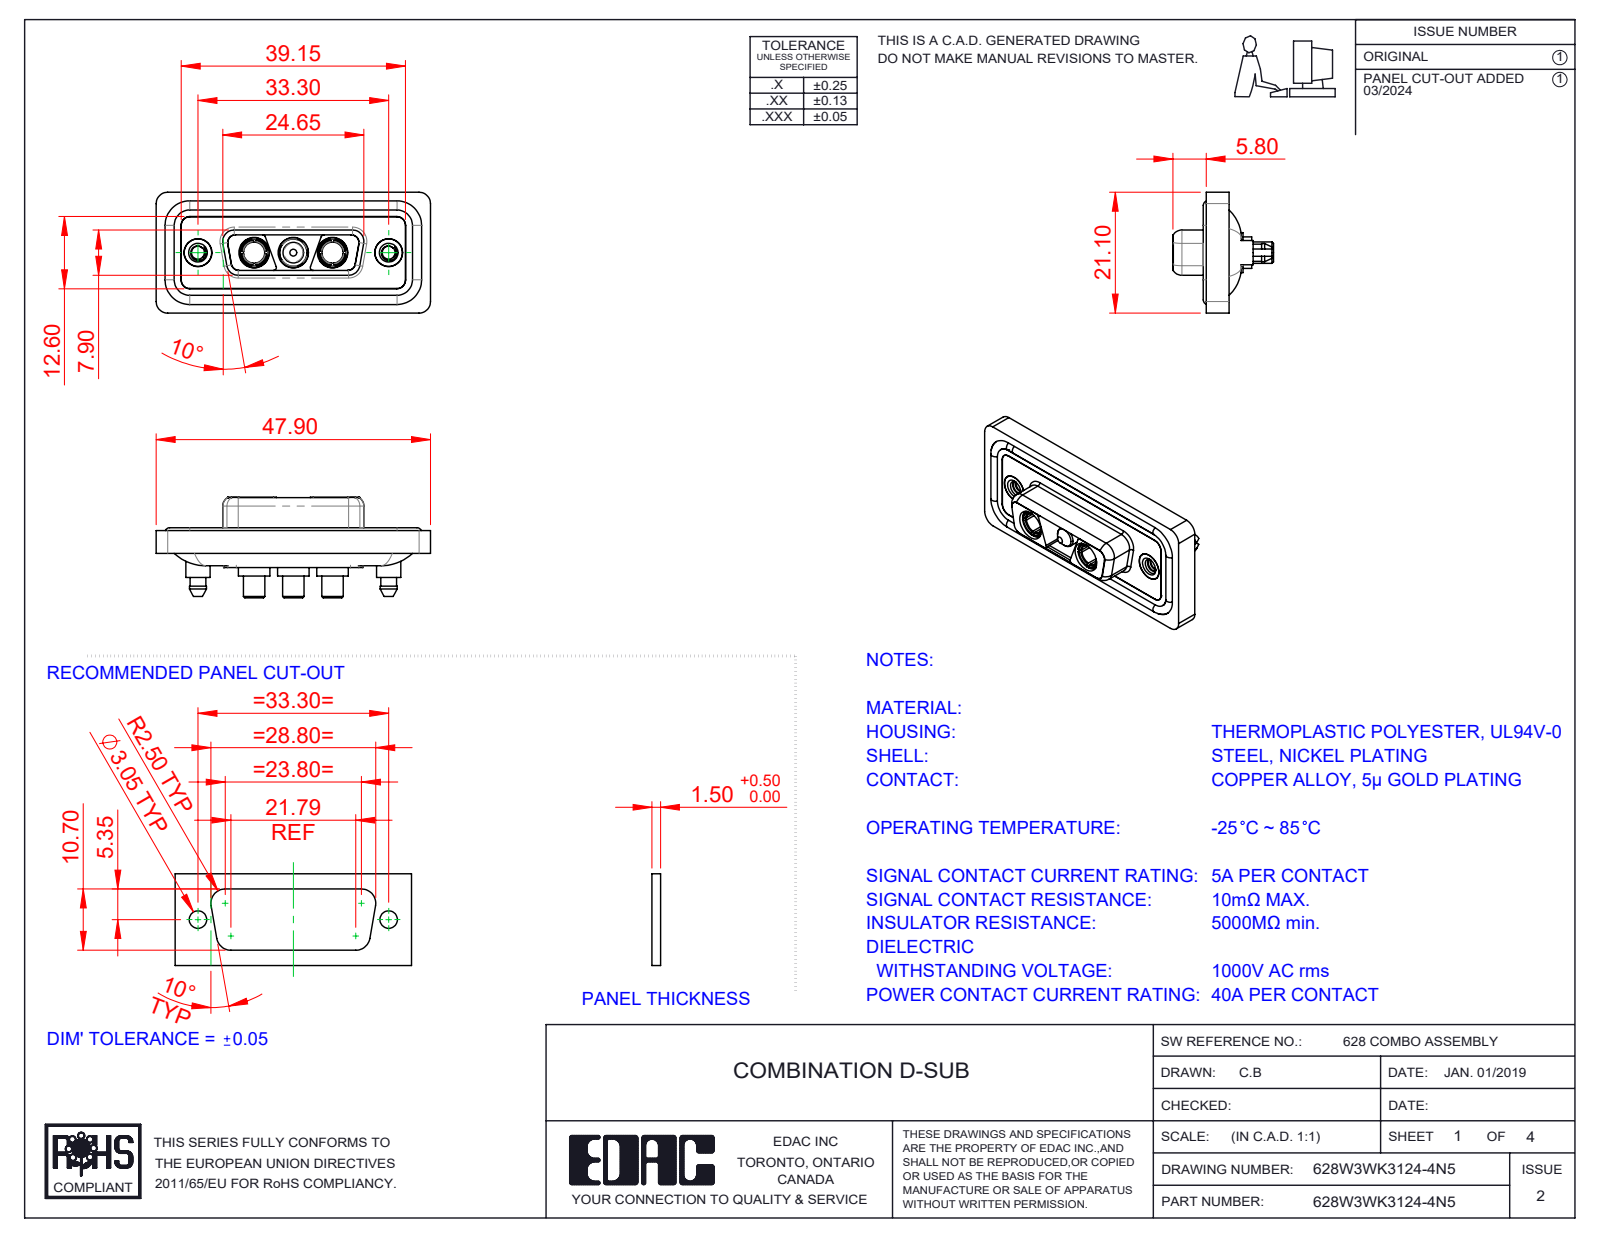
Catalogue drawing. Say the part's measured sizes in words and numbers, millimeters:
The part is named "Power Pin_40A S; 628Combo Housing_3WK3; 628Combo Shell Rear_15 Contacts; Power Socket_40A S (+4 more)". Its 3-D file was written by "SolidWorks 2023 (CONFIG_CONTROL_DESIGN)". It is 13 solids with 633 faces: 194 planar, 290 cylindrical and 149 other. Overall it measures 47.9 by 21.1 by 17.55 millimeters. Its volume is 6 067 cubic millimeters and its surface area 9 870 square millimeters. Round holes: 5 of diameter 4.85, 3 of diameter 5.3, 2 of diameter 2.26, 2 of diameter 3.7, 2 of diameter 4, 2 of diameter 4.05, 2 of diameter 5. Round bosses or shafts: 4 of diameter 1.6, 3 of diameter 5.5, 3 of diameter 5.2, 3 of diameter 4.75, 3 of diameter 3.75, 2 of diameter 5.4, 2 of diameter 4.96, 2 of diameter 4.95. Partial cylindrical surfaces (rounded edges, fillets, slot ends): 24 of radius 1.5, 20 of radius 2, 12 of radius 1.35, 10 of radius 1.6, 8 of radius 0.5, 4 of radius 0.25, 4 of radius 0.6, 4 of radius 0.65. The main face-to-face distances are 0.4, 1.6, 0.5, 1.8, 1.1, 2.9, 5.65, 7.05, 5.35, 1.5. The hole center spacings are 6.85, 9.8, 16.65, 23.5, 13.7, 33.3.
